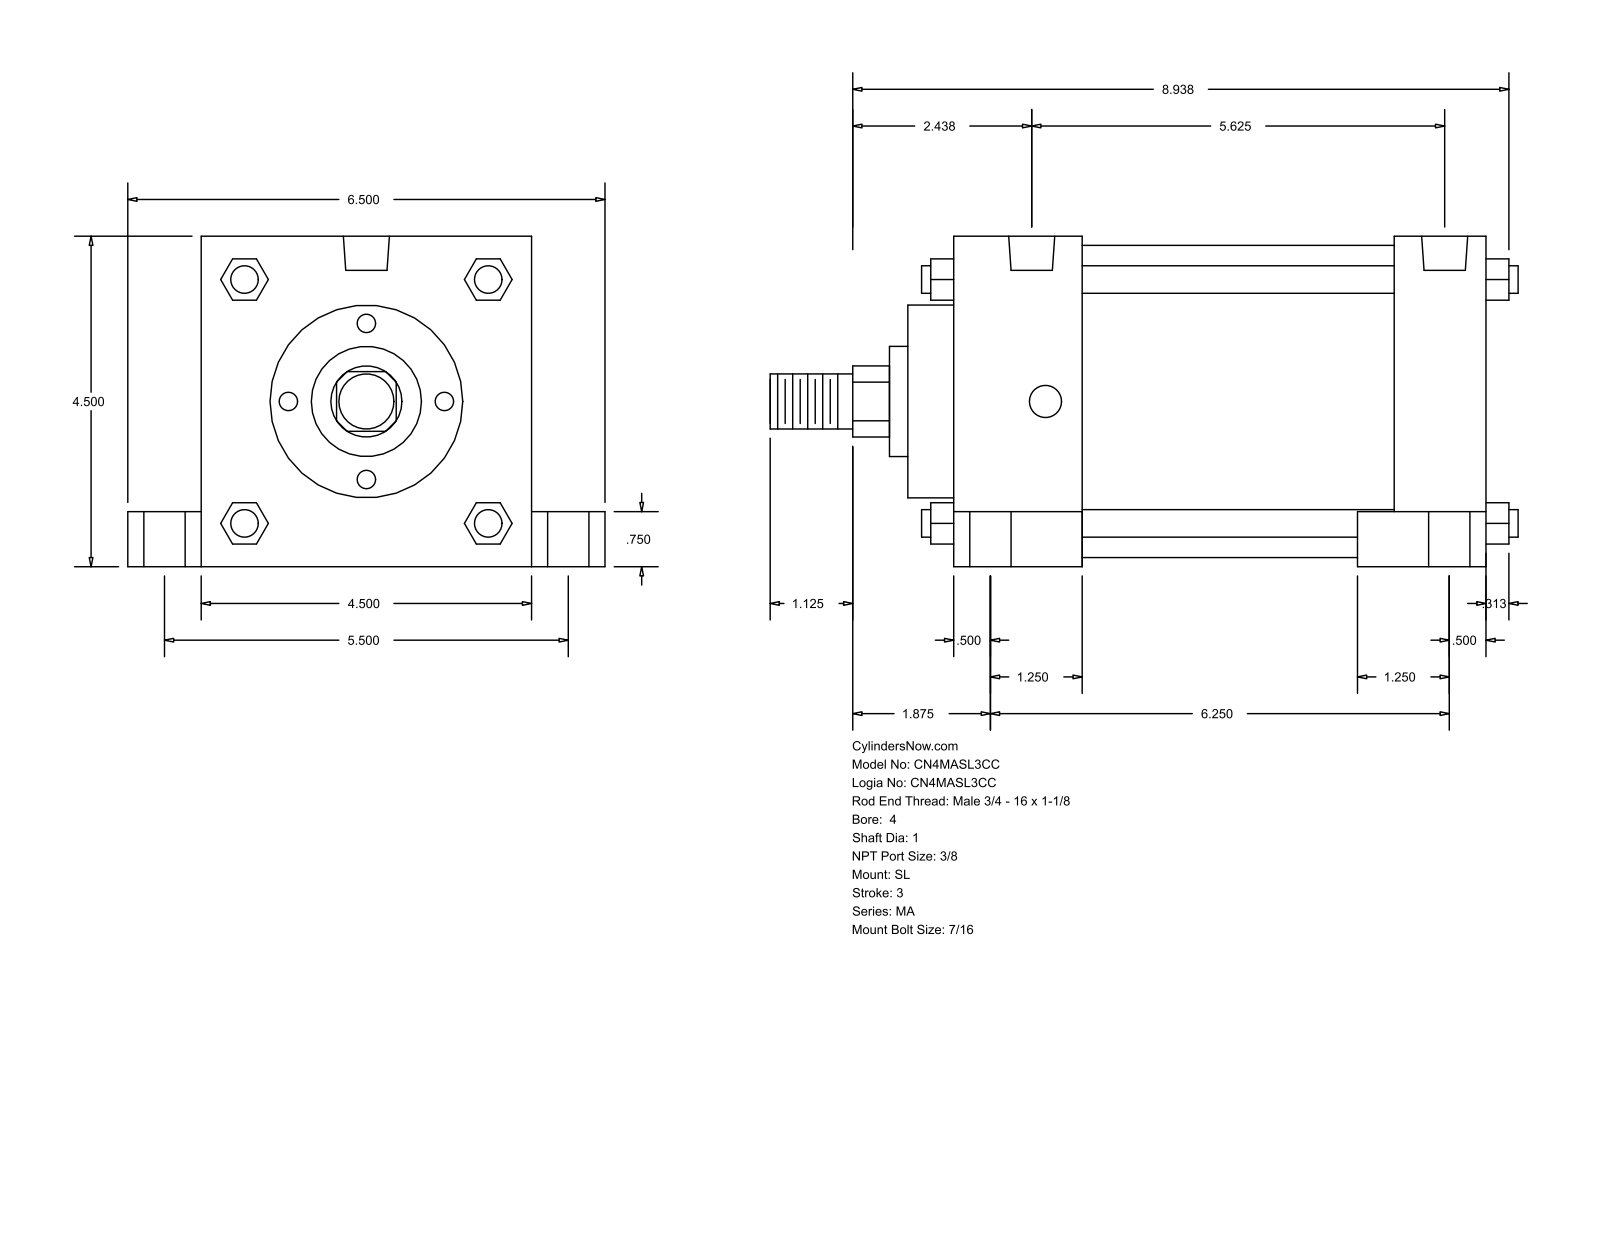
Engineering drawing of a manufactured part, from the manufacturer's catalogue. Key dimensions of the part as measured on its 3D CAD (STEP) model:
Part name (STEP PRODUCT): MA_SL__0400_1
STEP written by: GSSL Pune (CONFIG_CONTROL_DESIGN)
Units: millimetres
Bodies: 0 solids, 150 faces (113 planar, 37 cylindrical, 0 other)
Overall size (bounding box): 258.76 × 165.1 × 114.3
Round holes (diameter × count): ⌀11.11 ×4, ⌀14.29 ×4, ⌀20.64 ×4, ⌀15.93 ×2
Round bosses / shafts (diameter × count): ⌀9.53 ×4, ⌀107.95 ×1, ⌀66.67 ×1, ⌀38.1 ×1, ⌀25.4 ×1, ⌀19.05 ×1
Partial cylindrical surfaces — rounded edges, fillets, slot ends (radius × count): R12.29 ×1
Main face-to-face distances: 114.3, 184.15, 44.46, 139.69, 152.4, 107.94, 31.75, 25.4, 139.7, 200.02
Hole centre spacings: 4.76, 69.87, 70.14, 71.3, 72.4, 133.36, 138.12, 139.7
